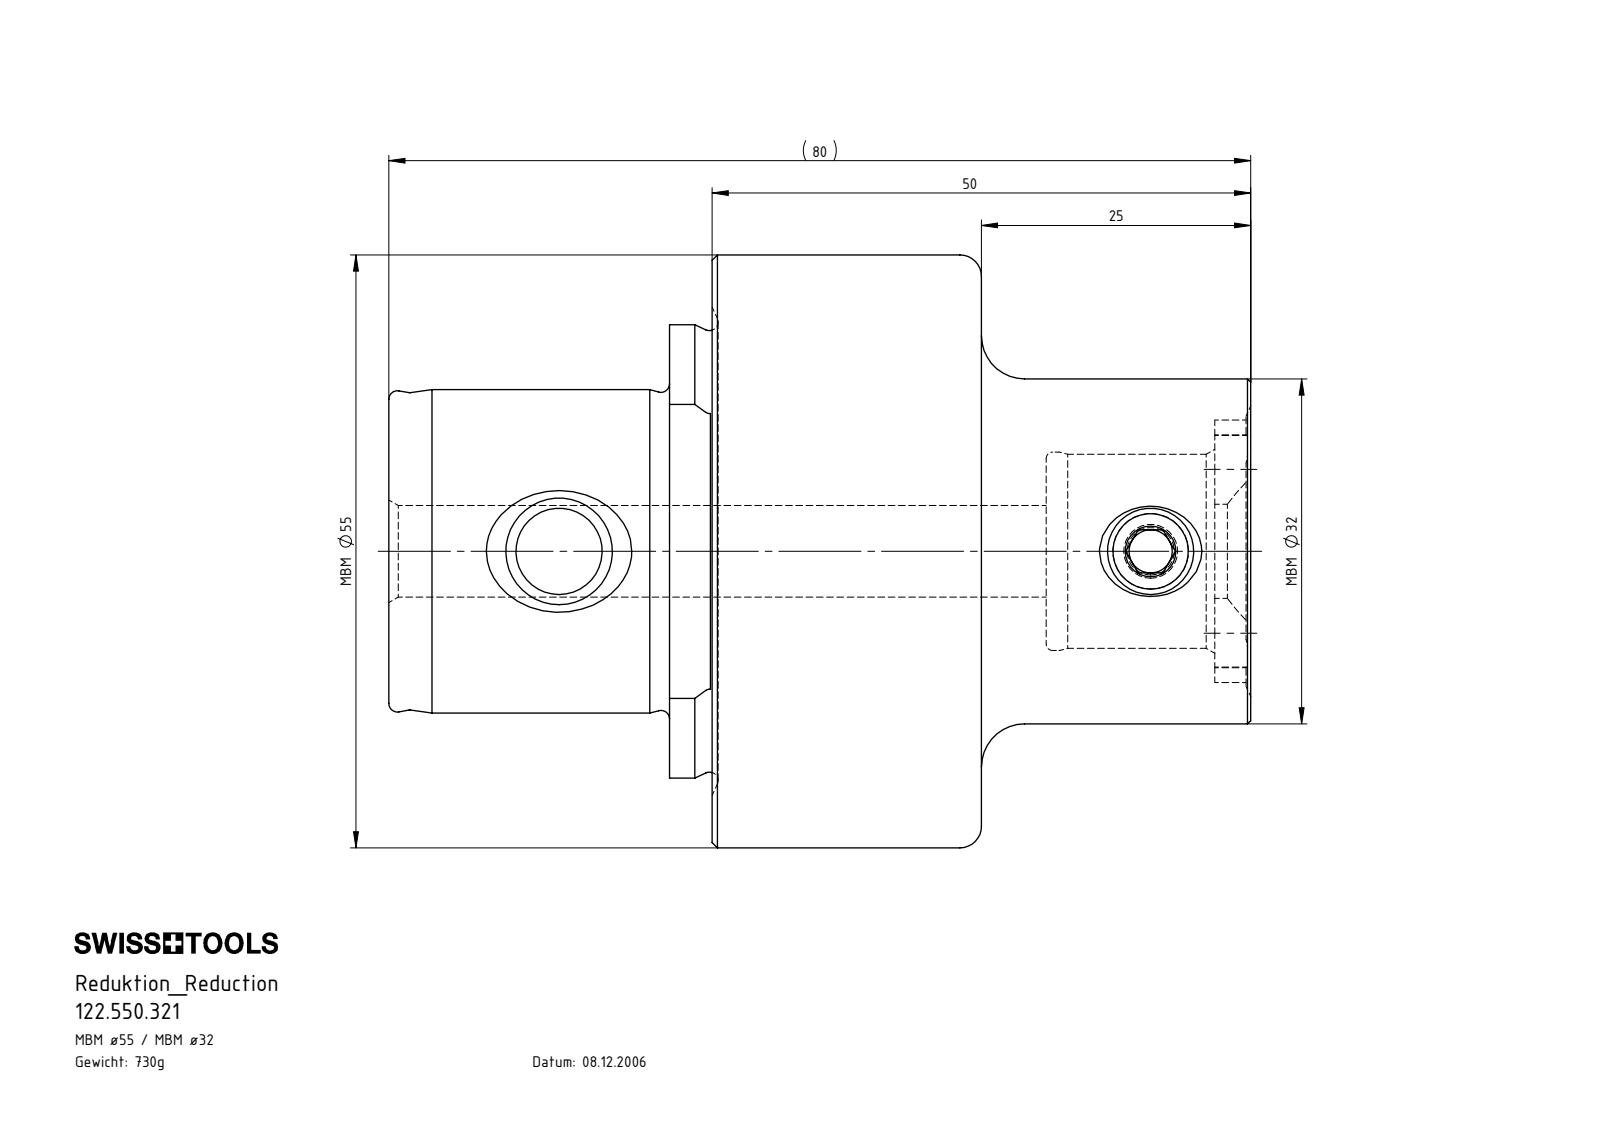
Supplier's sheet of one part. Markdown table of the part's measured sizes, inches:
| quantity | value |
| --- | --- |
| part name | MB5-MB3.K01.050_C; MB3-ER1.001.011_A; 122.550.321 |
| STEP written by | SolidWorks 2017 (CONFIG_CONTROL_DESIGN) |
| units | inches |
| bodies | 2 solids, 134 faces (33 planar, 34 cylindrical, 67 other) |
| overall size | 3.15 × 2.165 × 2.165 |
| volume | 5.677 in³ |
| surface area | 26.94 in² |
| round holes (diameter × count) | 0.157 × 1, 0.276 × 1, 0.315 × 1, 0.335 × 1, 0.709 × 1, 0.724 × 1 |
| round bosses / shafts (diameter × count) | 2.165 × 1, 1.26 × 1, 1.181 × 1, 0.315 × 1 |
| partial cylindrical surfaces (radius × count) | 0.126 × 4, 0.413 × 1, 0.48 × 1, 0.828 × 1 |
| main face-to-face distances | 0.984, 1.181, 2.165, 1.026, 0.156, 1.14, 3.15, 2.124, 1.969, 2.402 |
| hole center spacings | 2.161 |
